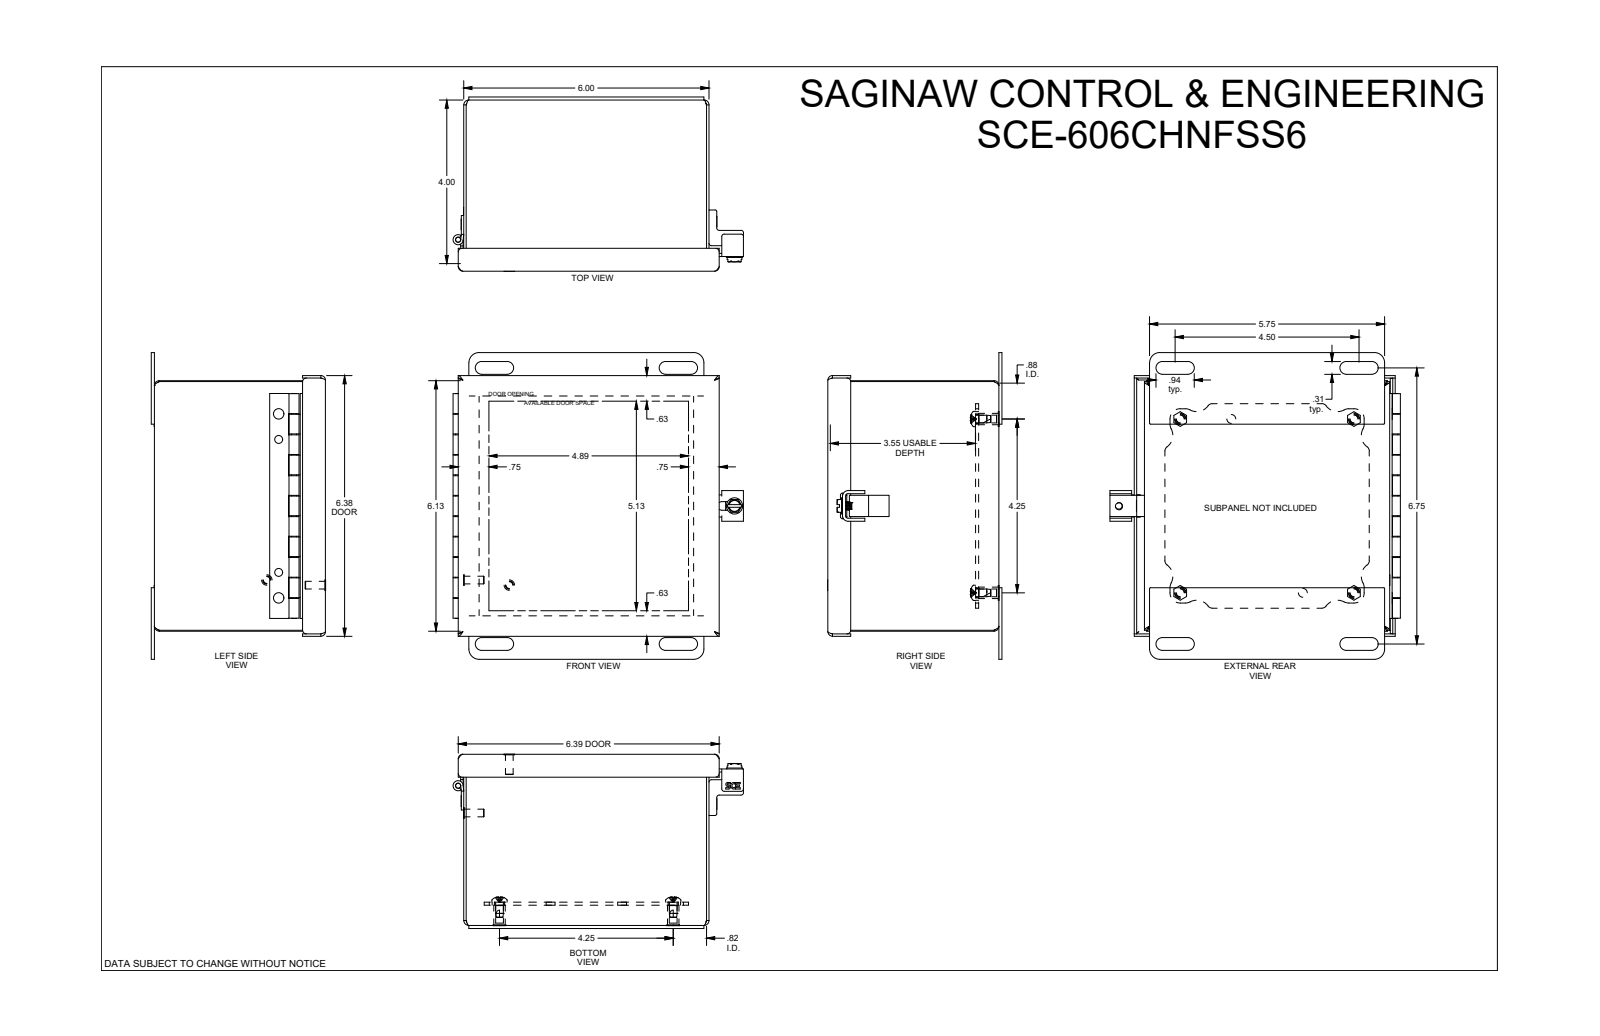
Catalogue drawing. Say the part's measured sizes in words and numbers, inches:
The part is named "SCE-606CHNFSS6". Its 3-D file was written by "SolidWorks 2019 (CONFIG_CONTROL_DESIGN)". It is 0 solids with 1010 faces: 467 planar, 275 cylindrical and 268 other. Overall it measures 7.5 by 7.104 by 4.265 inches. Round holes: 7 of diameter 0.19, 5 of diameter 0.193, 4 of diameter 0.25, 4 of diameter 0.281, 2 of diameter 0.193, 2 of diameter 0.218, 1 of diameter 0.126, 1 of diameter 0.156, 1 of diameter 0.266. Round bosses or shafts: 10 of diameter 0.188, 5 of diameter 0.256, 4 of diameter 0.373, 4 of diameter 0.28, 1 of diameter 0.396, 1 of diameter 0.246, 1 of diameter 0.123. Partial cylindrical surfaces (rounded edges, fillets, slot ends): 42 of radius 0.01, 17 of radius 0.06, 16 of radius 0.25, 8 of radius 0.007, 8 of radius 0.052, 8 of radius 0.112, 8 of radius 0.125, 8 of radius 0.156. The main face-to-face distances are 0.06, 5.94, 4.125, 6.065, 0.06, 4.185, 4.125, 4.065, 0.075, 6. The hole center spacings are 4.25, 1.25, 2.251, 3, 4.43, 5.202, 6.01, 0.305.
